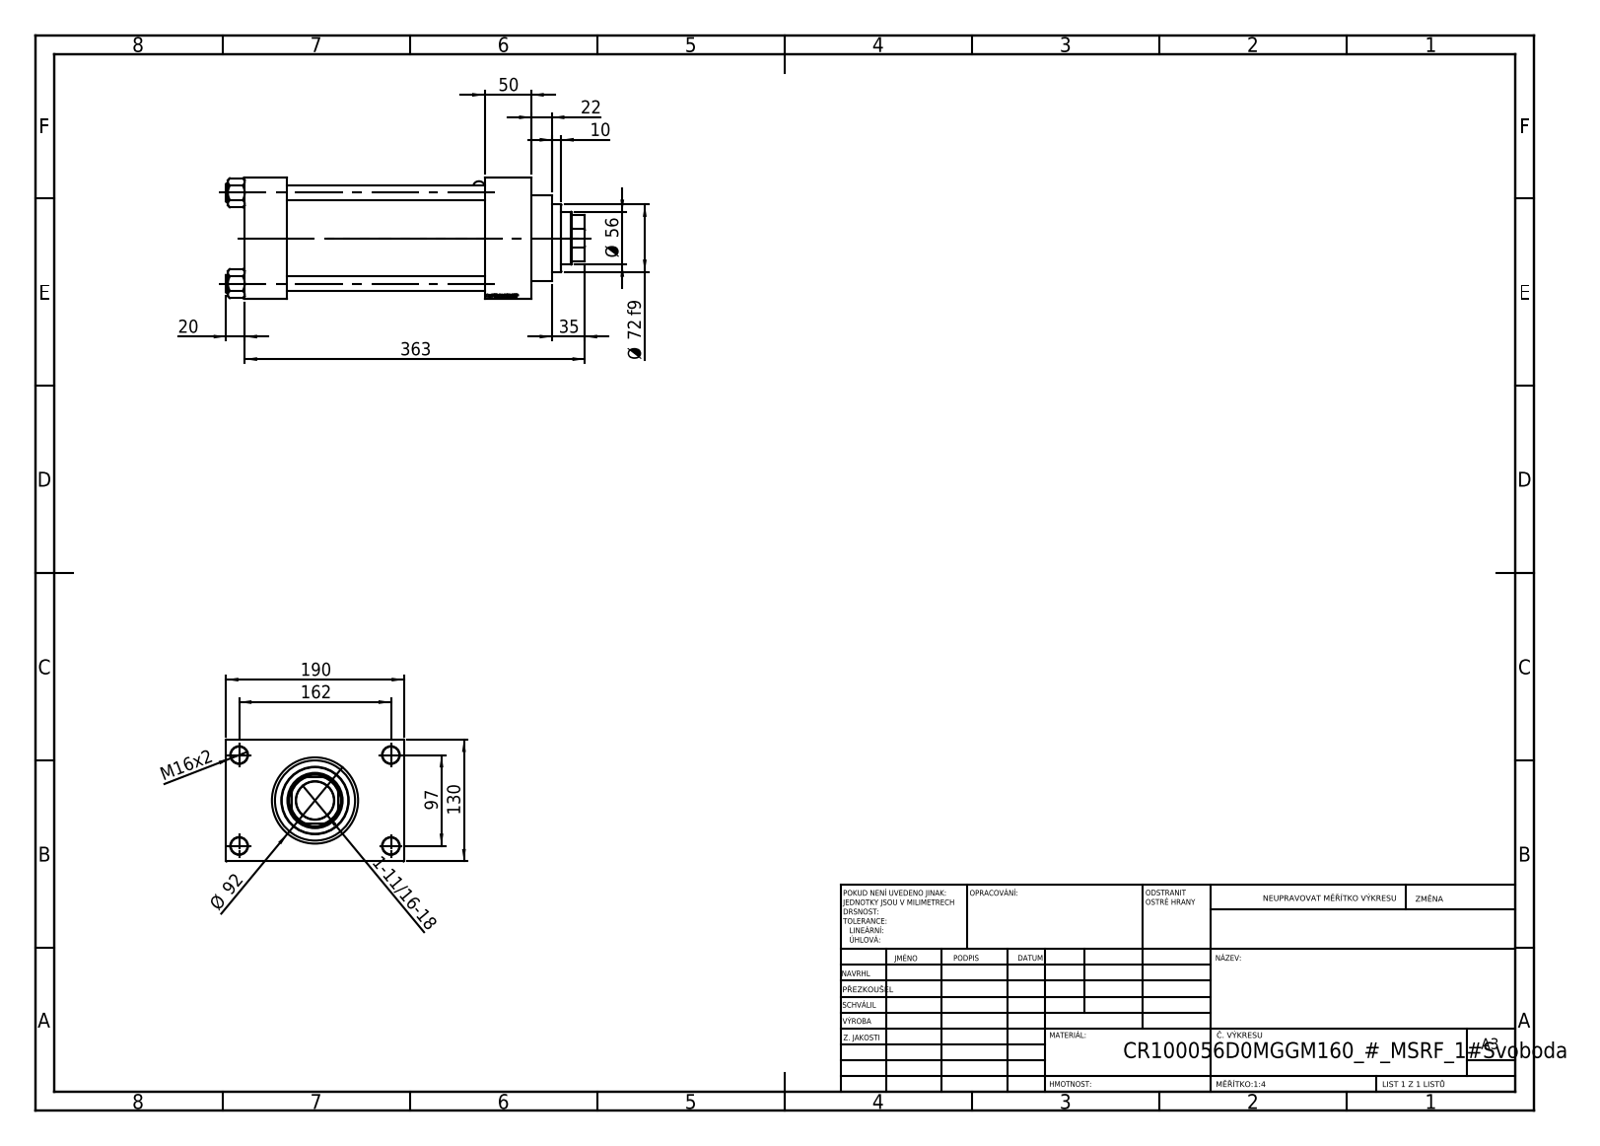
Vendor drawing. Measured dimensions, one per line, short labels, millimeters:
name: V215CR_D_Body; MSRF_MSRG1; NUT_M5_D; V215CR_VCP_D (+2 more)
written by: SolidWorks 2019 (CONFIG_CONTROL_DESIGN)
unit: mm
bodies: 12 solids, 1184 faces (563 planar, 103 cylindrical, 518 other)
size: 383 × 190 × 130
volume: 3 242 000 mm³; area: 505 617 mm²
holes: 4× ⌀16, 4× ⌀18, 2× ⌀7, 2× ⌀26.44, 2× ⌀35, 1× ⌀40.5, 1× ⌀56, 1× ⌀59, 1× ⌀76, 1× ⌀85.5, 1× ⌀100
bosses: 4× ⌀19, 1× ⌀106, 1× ⌀92, 1× ⌀72, 1× ⌀5, 1× ⌀2.5
rounds: 6× R0.5, 2× R6, 1× R27
face distances: 130, 50, 45, 256, 211, 160, 306, 261, 30, 190
hole spacings: 32.55, 68.52, 94.41, 96.9, 102.27, 129.45, 161.73, 97
